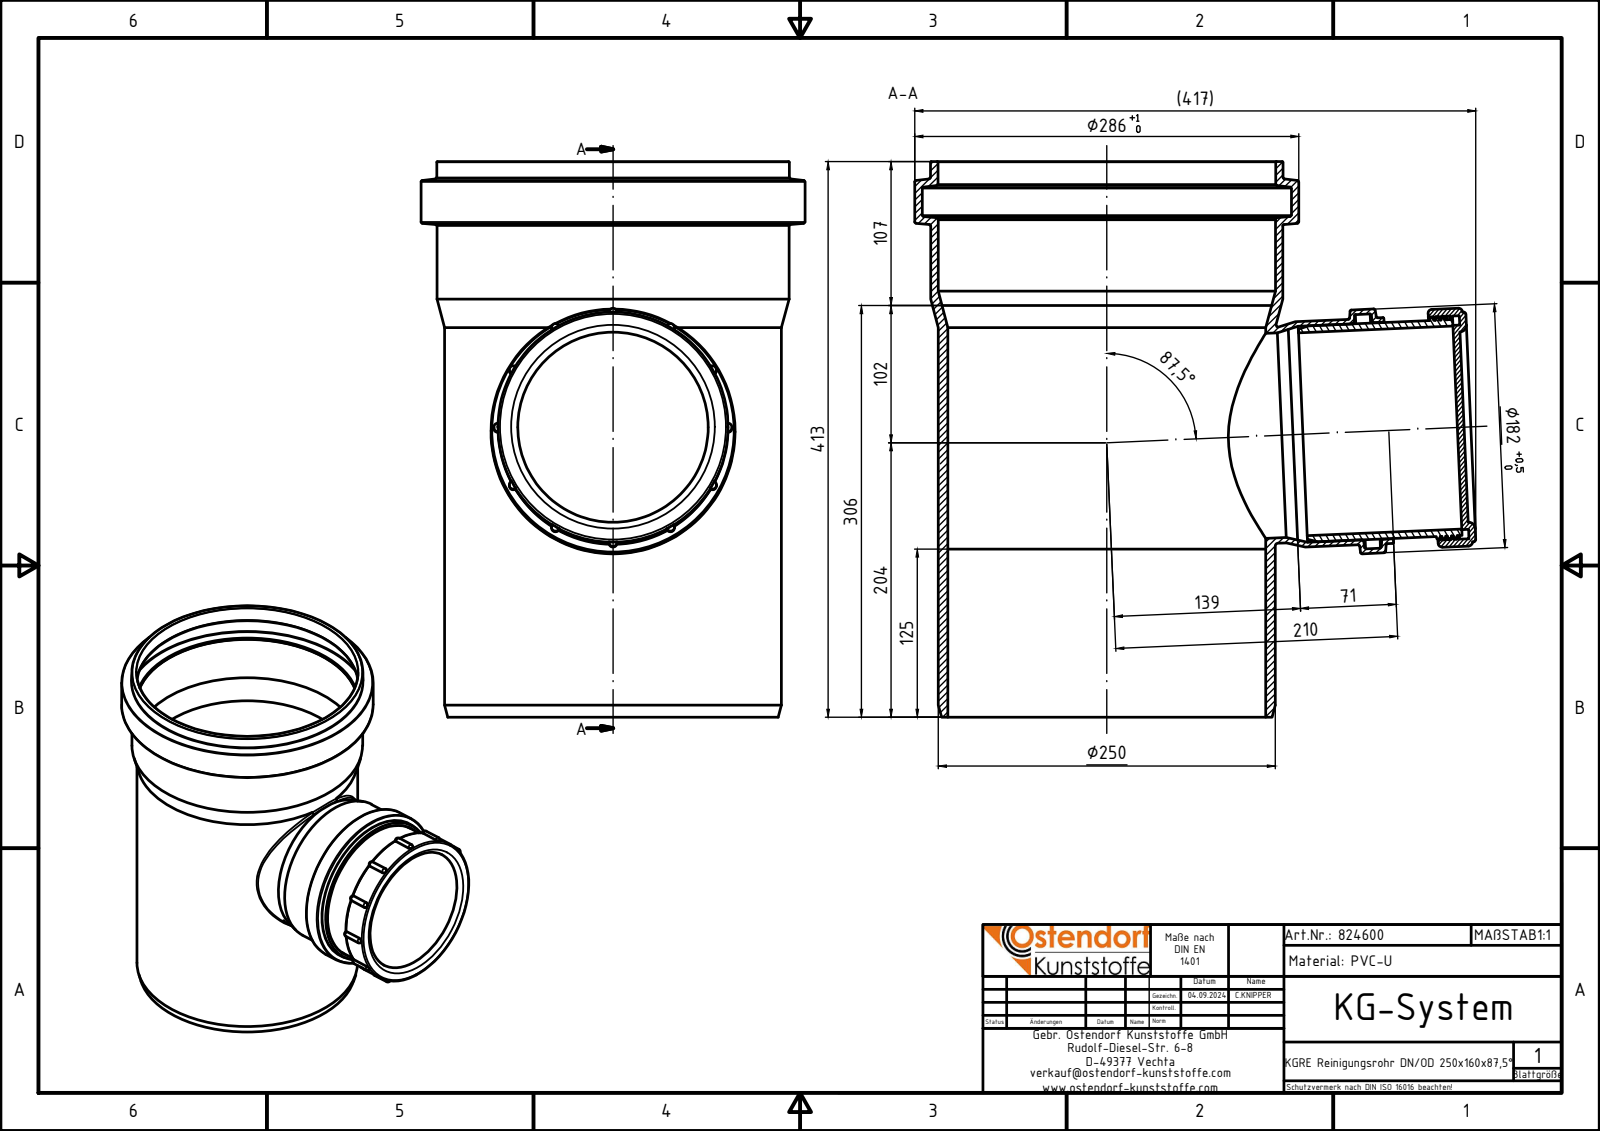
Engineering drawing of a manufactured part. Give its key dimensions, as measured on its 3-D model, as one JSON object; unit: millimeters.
{"part_name": "824600z; 824600z Rohr; 824600z Deckel; 824600z Einsatz", "step_written_by": "Autodesk Inventor 2024 (AUTOMOTIVE_DESIGN)", "units": "millimeters", "bodies": {"solids": 3, "faces": 155, "planar": 13, "cylindrical": 49, "other": 93}, "overall_size": [417.06, 413, 285.5], "volume_mm3": 2761000, "surface_area_mm2": 969558, "round_holes": [[161.1, 2], [151, 1], [152.3, 1], [160.7, 1], [162.3, 1], [166, 1], [174.4, 1], [236.3, 1], [250.8, 1], [251.1, 1], [274.5, 1]], "round_bosses_or_shafts": [[285.5, 1], [262.1, 1], [261.8, 1], [250.5, 1], [181.4, 1], [171, 1], [168.1, 1], [167.7, 1]], "partial_cylinders_radius": [[3, 12]], "face_to_face_distances": [4.97, 5, 5.03, 10, 413, 5.06, 10.06, 115, 115.06, 120.03]}
